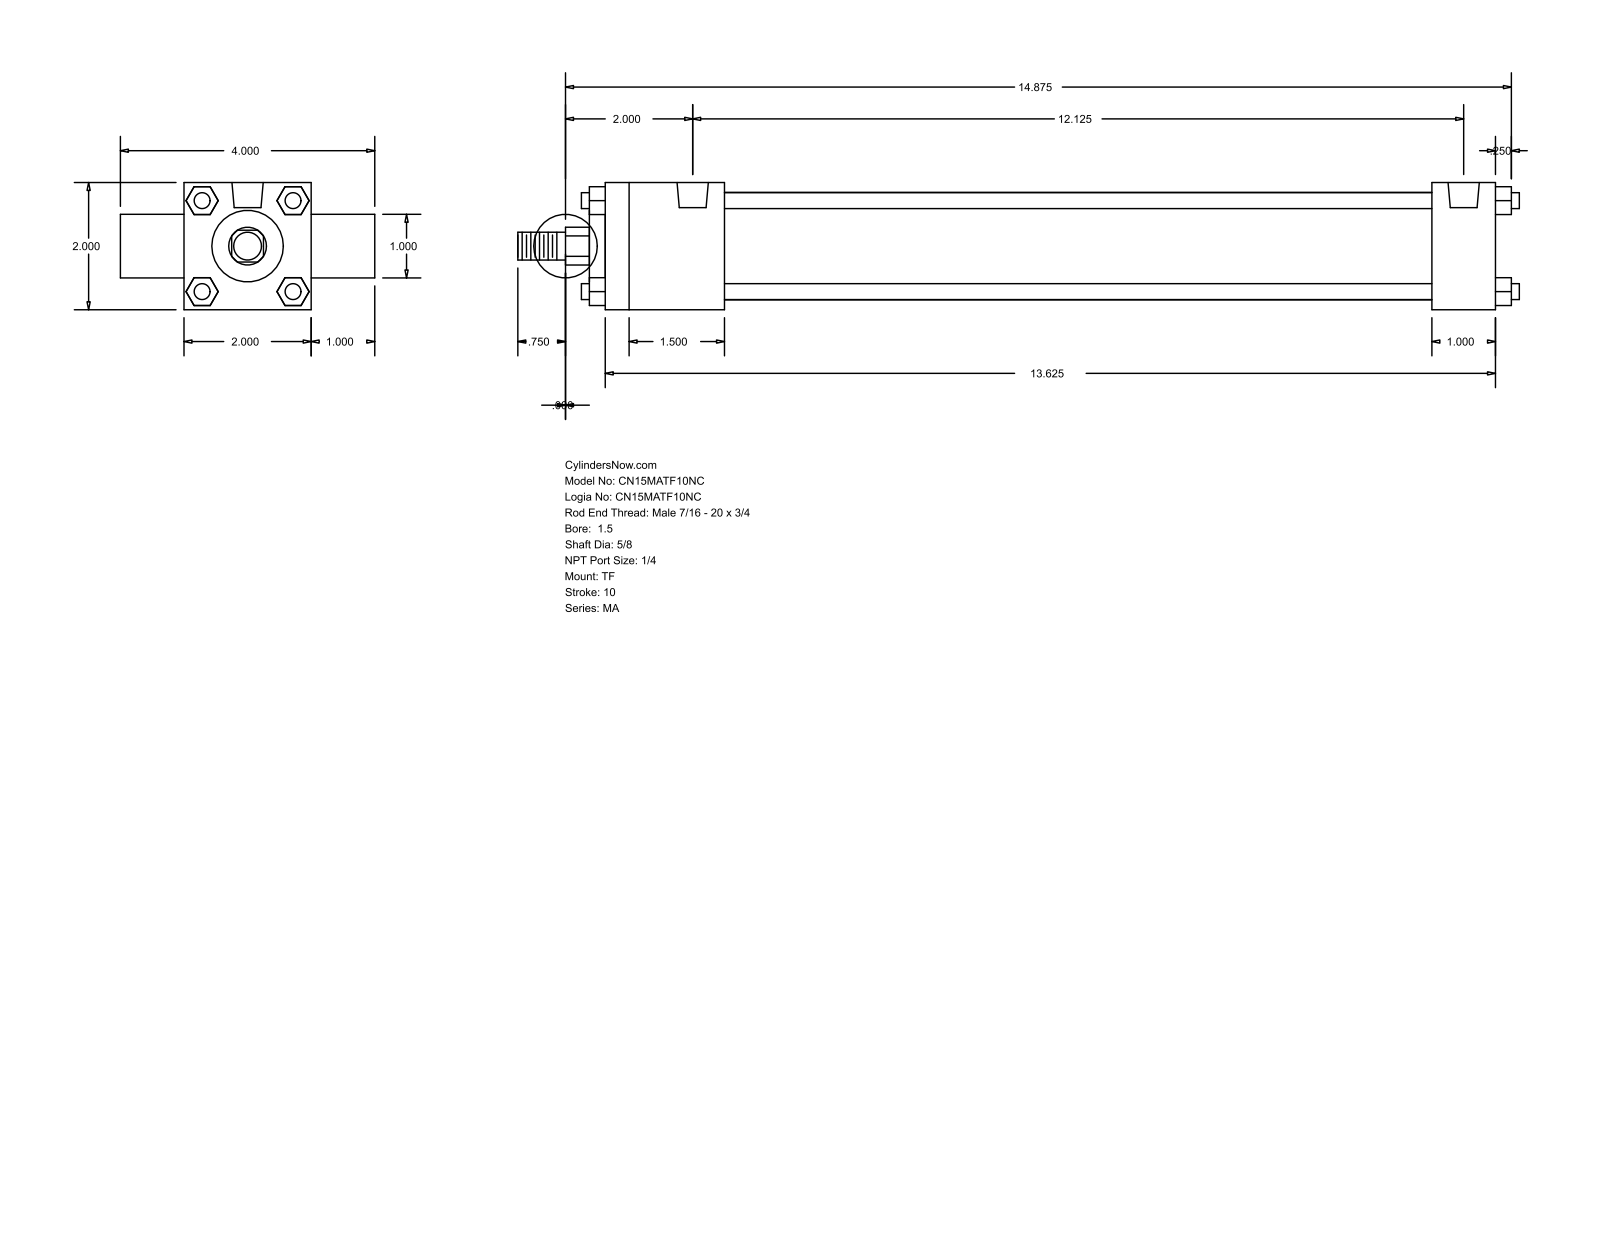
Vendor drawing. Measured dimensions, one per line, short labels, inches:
name: MA_TF__0150_0.625
written by: GSSL Pune (CONFIG_CONTROL_DESIGN)
unit: in
bodies: 0 solids, 120 faces (92 planar, 28 cylindrical, 0 other)
size: 15.75 × 4 × 2
holes: 3× ⌀0.313, 2× ⌀0.492
bosses: 4× ⌀0.25, 1× ⌀1.69, 1× ⌀1.125, 1× ⌀1, 1× ⌀0.625, 1× ⌀0.437
rounds: 1× R0.297
face distances: 2, 14, 1, 3, 1.875, 13, 11.125, 12.125, 1, 0.25
hole spacings: 12.125
